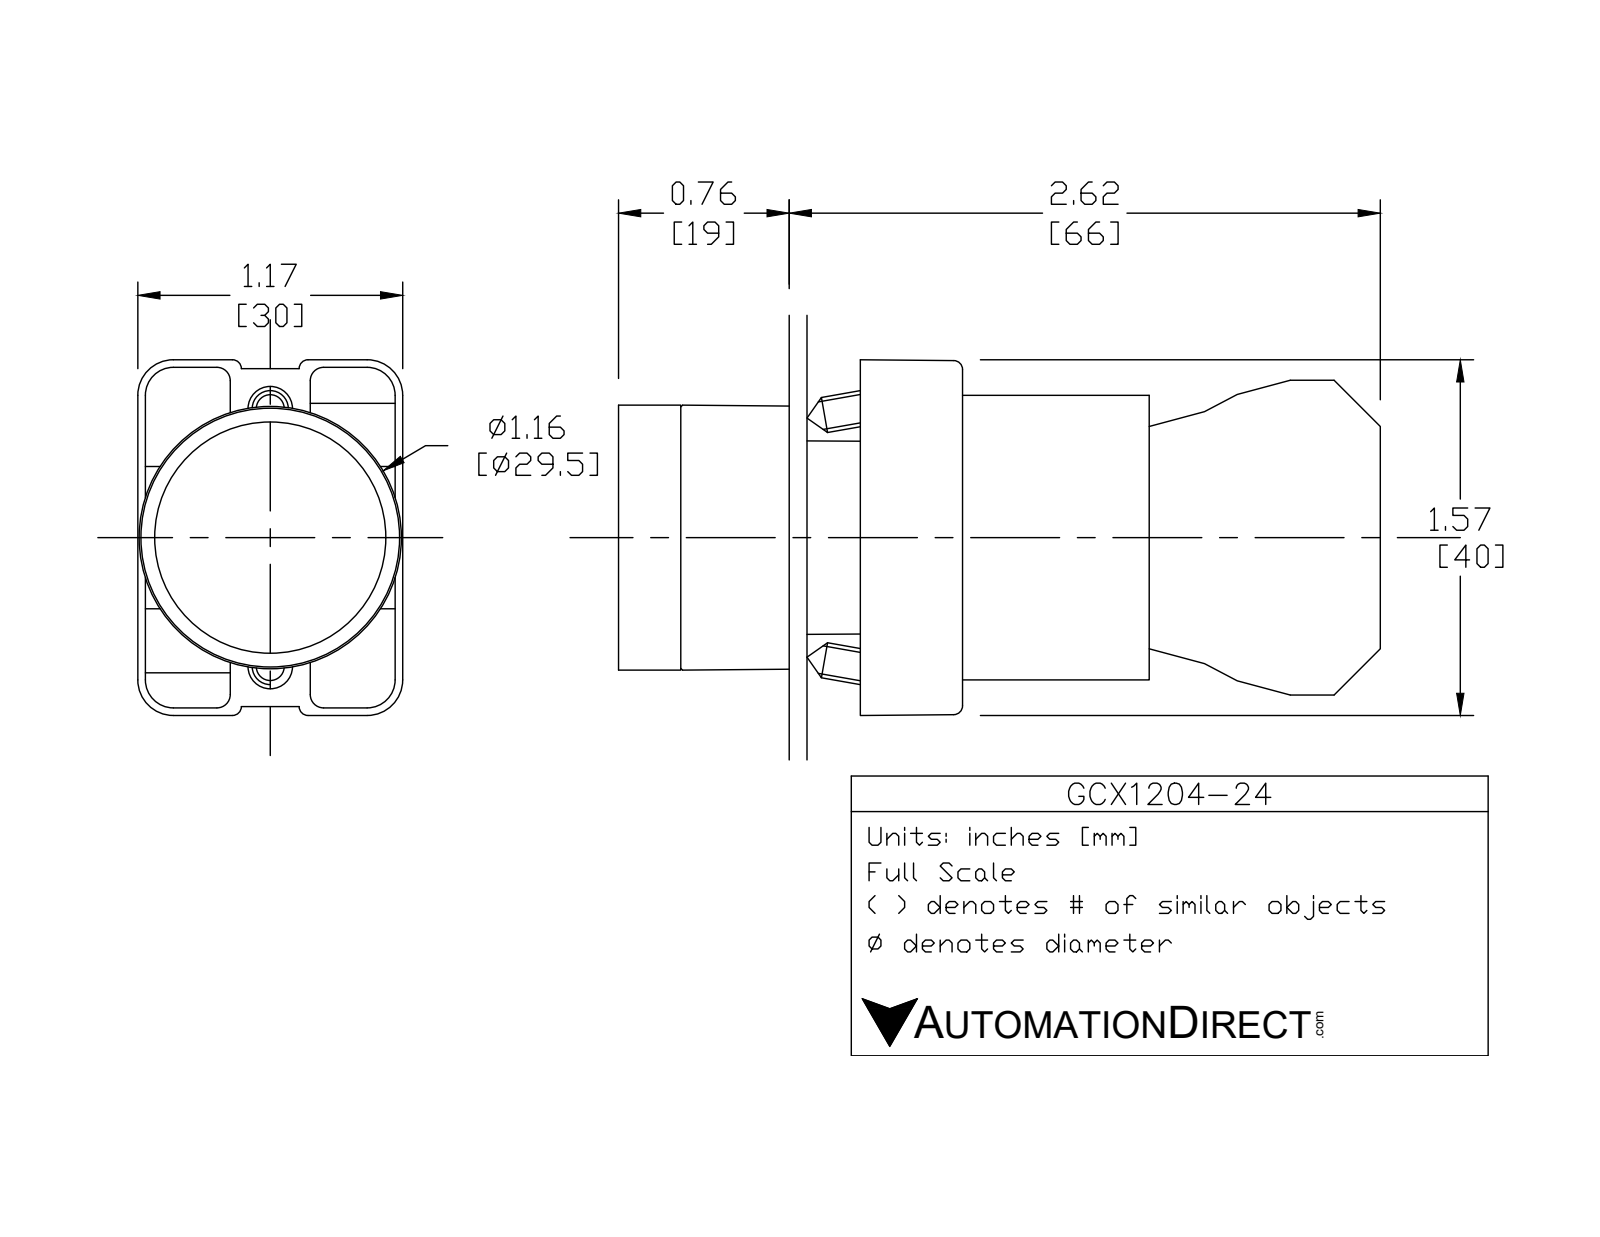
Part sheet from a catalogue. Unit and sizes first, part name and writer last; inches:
Units: inches
Overall size (bounding box): 3.319 × 1.581 × 1.177
Round holes (diameter × count): ⌀0.079 ×2, ⌀0.124 ×2, ⌀0.13 ×2, ⌀0.087 ×1, ⌀0.197 ×1, ⌀0.469 ×1, ⌀0.878 ×1, ⌀0.888 ×1, ⌀1.024 ×1
Round bosses / shafts (diameter × count): ⌀0.157 ×4, ⌀1.175 ×1, ⌀1.004 ×1, ⌀0.945 ×1, ⌀0.856 ×1, ⌀0.78 ×1, ⌀0.504 ×1
Partial cylindrical surfaces — rounded edges, fillets, slot ends (radius × count): R0.059 ×24, R0.041 ×12, R0.124 ×12, R0.157 ×12, R0.039 ×8, R0.128 ×2, R0.02 ×1, R0.063 ×1
Main face-to-face distances: 0.827, 2.02, 1.193, 0.579, 1.171, 0.031, 0.276, 0.033, 0.748, 0.573
Hole centre spacings: 0.236, 0.544, 0.472, 0.49
Volume: 2.794 in³ · Surface area: 38.75 in²
Bodies: 8 solids, 431 faces (252 planar, 148 cylindrical, 31 other)
Part name (STEP PRODUCT): GCX1204-24; ecx1040; GCX1204 OPERATOR; ECX1050 (+1 more)
STEP written by: SolidWorks 2016 (AUTOMOTIVE_DESIGN)
